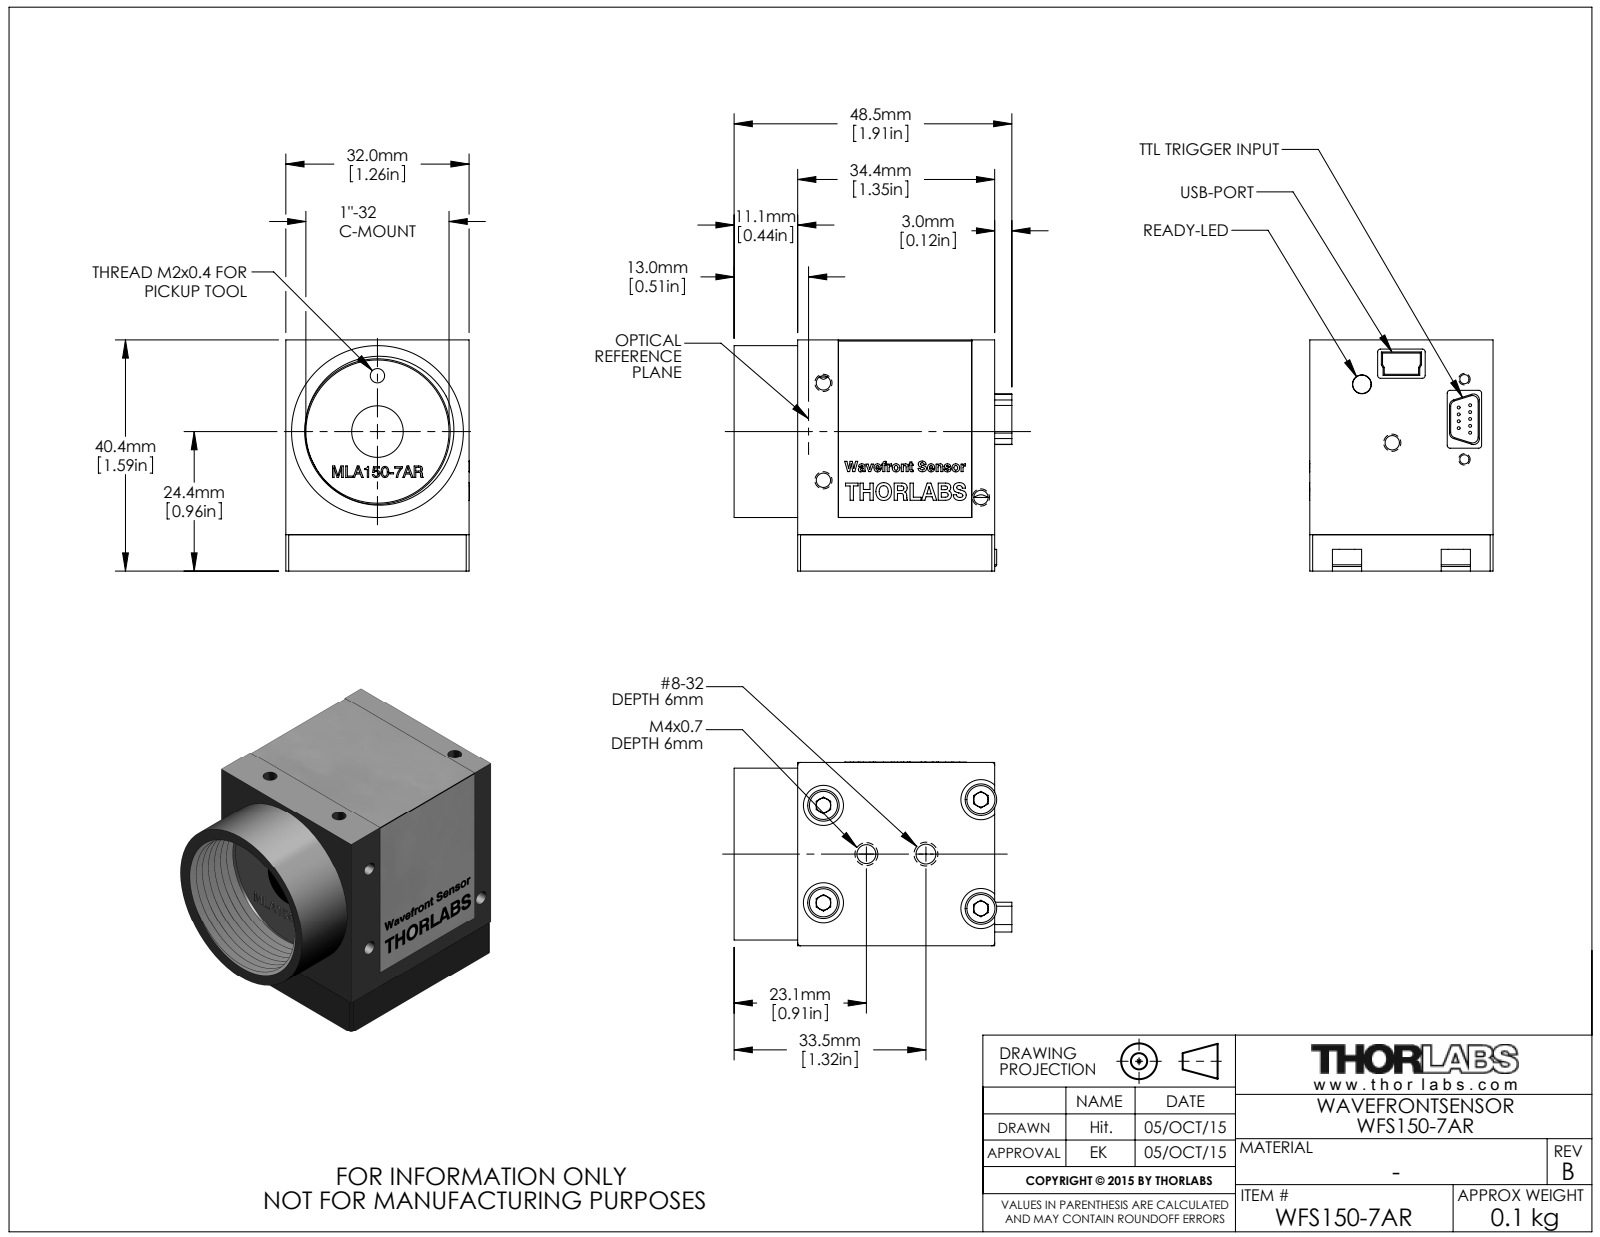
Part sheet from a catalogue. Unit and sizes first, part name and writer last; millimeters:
Units: millimetres
Overall size (bounding box): 48.5 × 40.35 × 32.05
Round holes (diameter × count): ⌀2.5 ×9, ⌀1.6 ×8, ⌀3.2 ×4, ⌀3.3 ×2, ⌀7 ×2, ⌀3.45 ×1, ⌀9 ×1, ⌀25 ×1
Round bosses / shafts (diameter × count): ⌀0.5 ×9, ⌀5.5 ×4, ⌀3 ×4, ⌀30 ×1, ⌀3.2 ×1
Partial cylindrical surfaces — rounded edges, fillets, slot ends (radius × count): R0.5 ×12, R1 ×8, R3.5 ×2
Main face-to-face distances: 34, 34.4, 6.35, 40.35, 31.8, 32, 3.8, 2.55, 36.55, 45.5
Hole centre spacings: 12, 3.2, 3.54, 6.36, 7, 8.28, 10.9, 11.24
Volume: 45 167 mm³ · Surface area: 14 759 mm²
Bodies: 7 solids, 1141 faces (612 planar, 141 cylindrical, 388 other)
Part name (STEP PRODUCT): 19905-E0W - Rev B
STEP written by: SolidWorks 2014 (AUTOMOTIVE_DESIGN)
